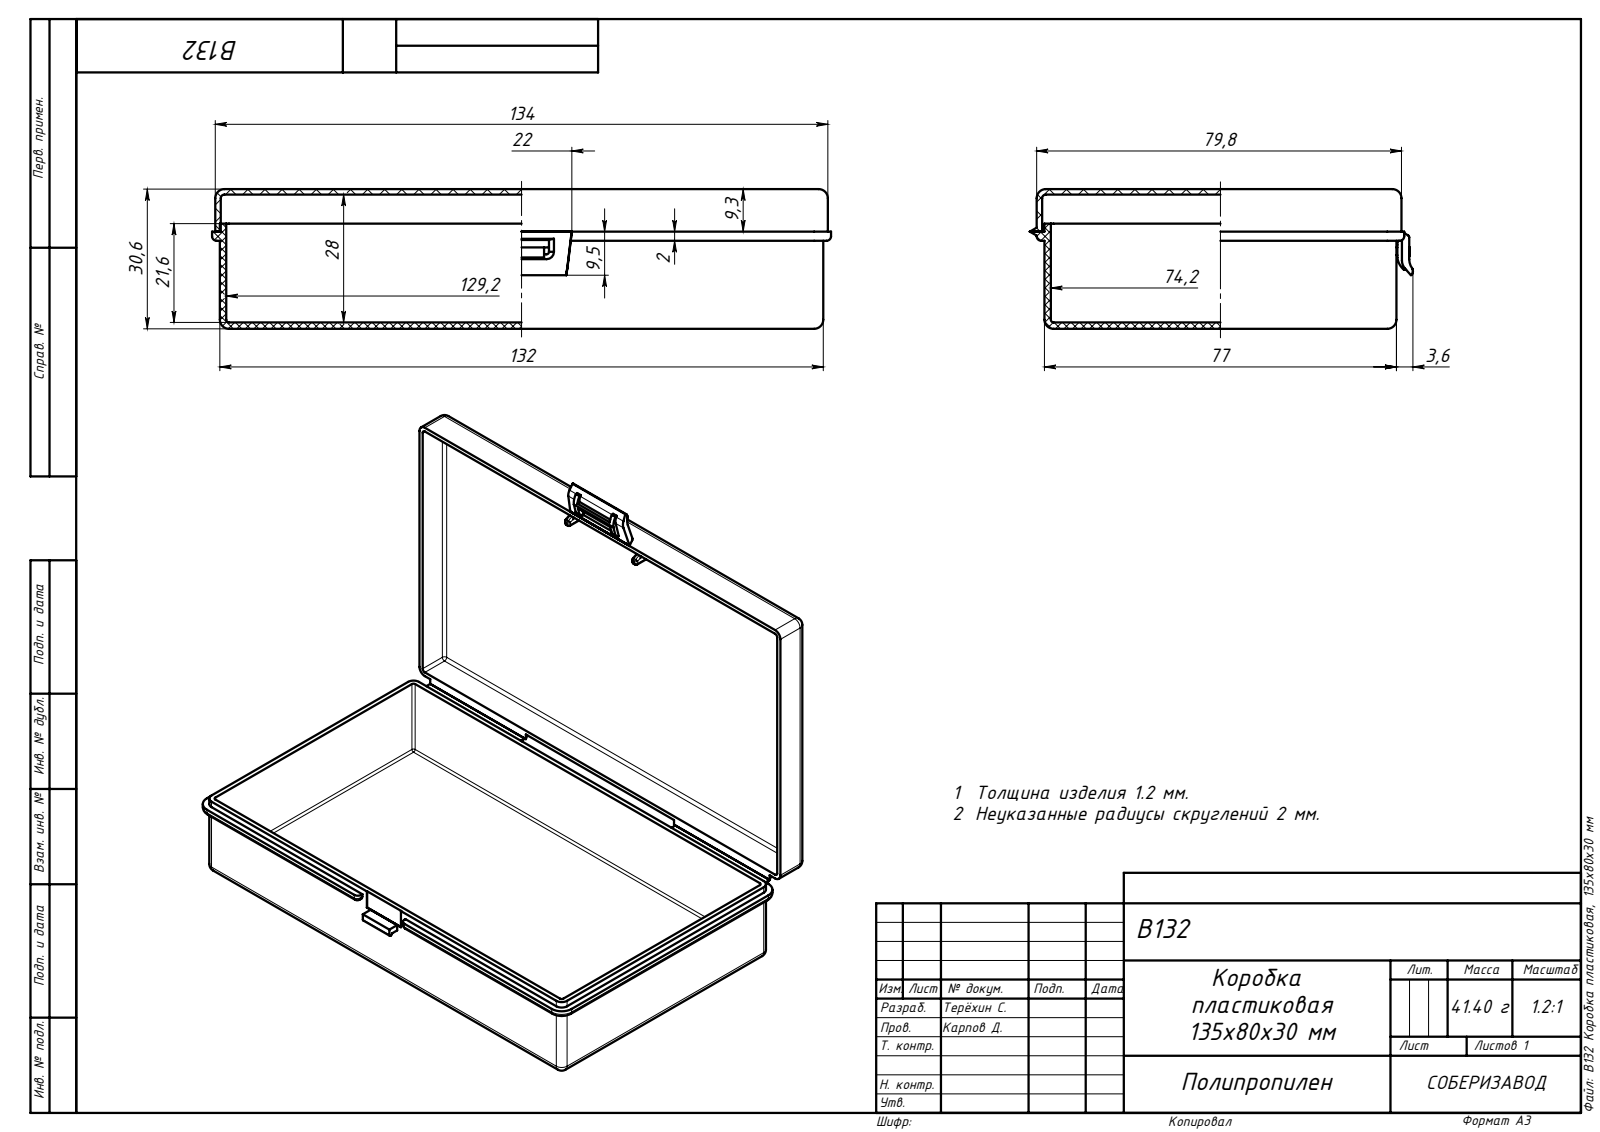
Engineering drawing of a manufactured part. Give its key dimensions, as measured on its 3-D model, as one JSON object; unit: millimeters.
{"part_name": "B132 Емкость_00; B132 Коробка пластиковая, 135x80x30 мм; B132 Крышка_12; B132 Защёлка_00", "step_written_by": "SolidWorks 2020 (AUTOMOTIVE_DESIGN)", "units": "millimeters", "bodies": {"solids": 7, "faces": 235, "planar": 107, "cylindrical": 88, "other": 40}, "overall_size": [135.4, 83.81, 30.55], "volume_mm3": 44668, "surface_area_mm2": 68673, "partial_cylinders_radius": [[2, 16], [0.5, 15], [0.6, 8], [0.8, 8], [0.7, 7], [1, 4], [1.3, 4], [3.7, 4]], "face_to_face_distances": [1.4, 1.2, 29.35, 30.55, 27.95, 29.15, 75.6, 130.6, 74.2, 77]}
